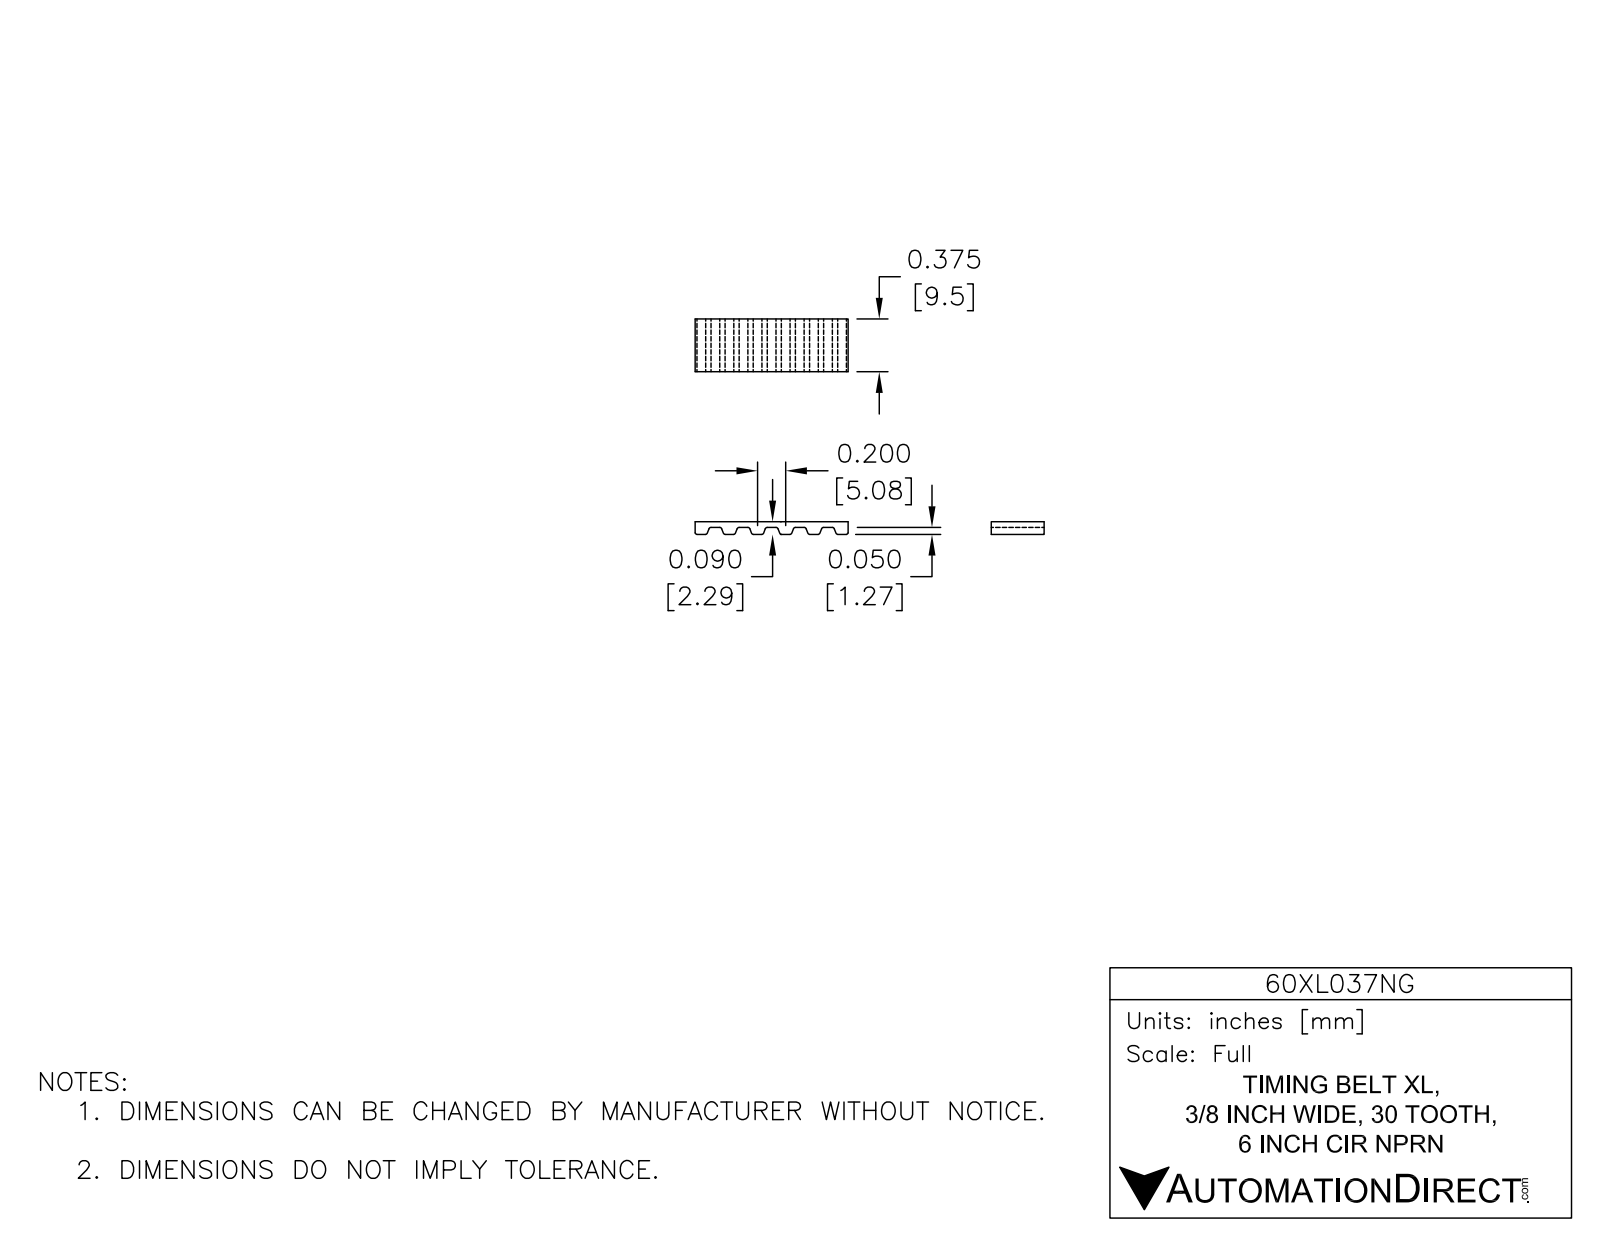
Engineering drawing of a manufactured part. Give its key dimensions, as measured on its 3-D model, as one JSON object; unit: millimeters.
{"part_name": "60XL037NG", "step_written_by": "SolidWorks 2014 (AUTOMOTIVE_DESIGN)", "units": "millimeters", "bodies": {"solids": 1, "faces": 258, "planar": 106, "cylindrical": 152, "other": 0}, "overall_size": [59.1, 30, 9.5], "volume_mm3": 1980, "surface_area_mm2": 3656, "partial_cylinders_radius": [[0.4, 120], [14, 2], [15, 2]], "face_to_face_distances": [30, 1, 29, 9.5, 4.4, 28, 8.8, 9.9, 13.2, 5.5]}
